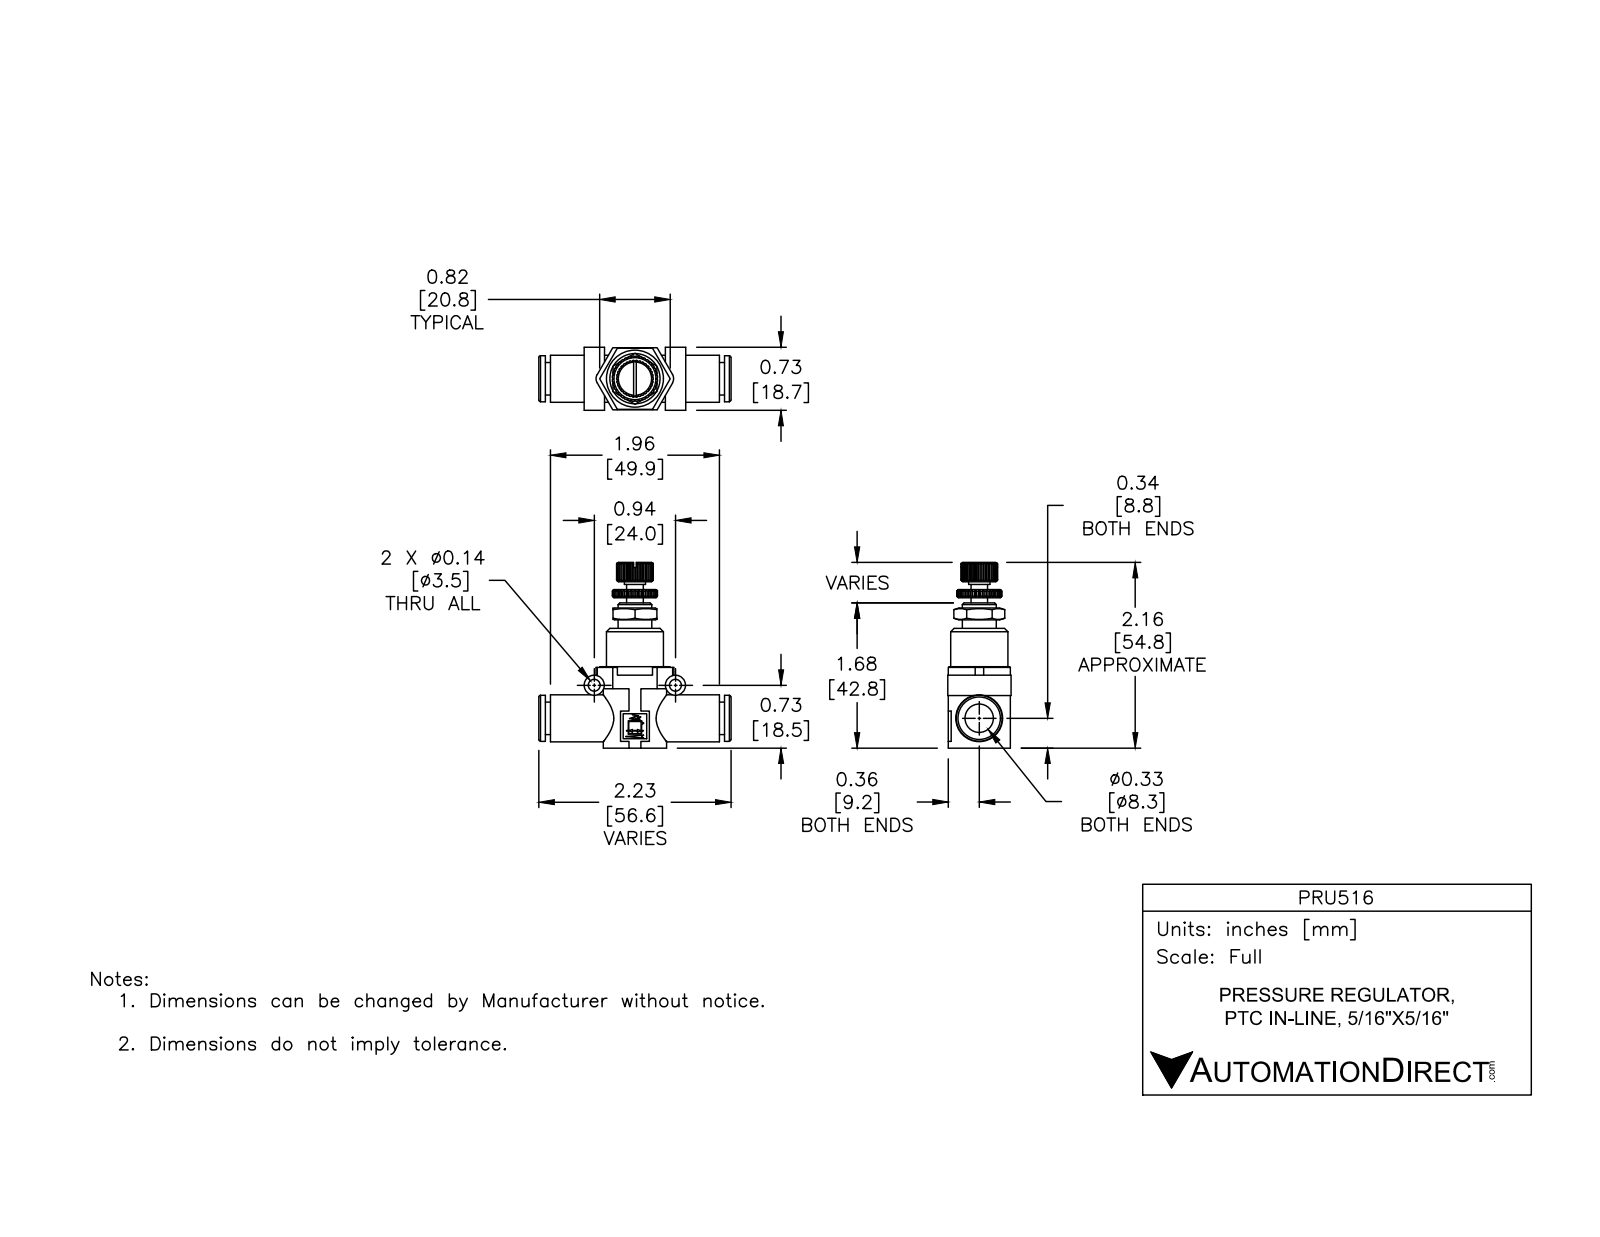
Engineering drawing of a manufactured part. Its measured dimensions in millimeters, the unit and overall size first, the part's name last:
Units: millimetres
Overall size (bounding box): 56.61 × 54.75 × 18.65
Round holes (diameter × count): ⌀3.5 ×2, ⌀8.3 ×1, ⌀9.75 ×1
Round bosses / shafts (diameter × count): ⌀6 ×2, ⌀18.65 ×1, ⌀16.85 ×1, ⌀13.85 ×1, ⌀13.55 ×1, ⌀10 ×1, ⌀9.6 ×1, ⌀6.25 ×1
Partial cylindrical surfaces — rounded edges, fillets, slot ends (radius × count): R2.5 ×2, R5.38 ×1, R6.65 ×1
Main face-to-face distances: 21.5, 1.5, 2.5, 25.25, 1.25, 19.25, 13.75, 18.32, 22.75, 11.5
Hole centre spacings: 24
Volume: 14 948 mm³ · Surface area: 9 801 mm²
Bodies: 4 solids, 412 faces (276 planar, 116 cylindrical, 20 other)
Part name (STEP PRODUCT): PRU516
STEP written by: SolidWorks 2015 (CONFIG_CONTROL_DESIGN)
